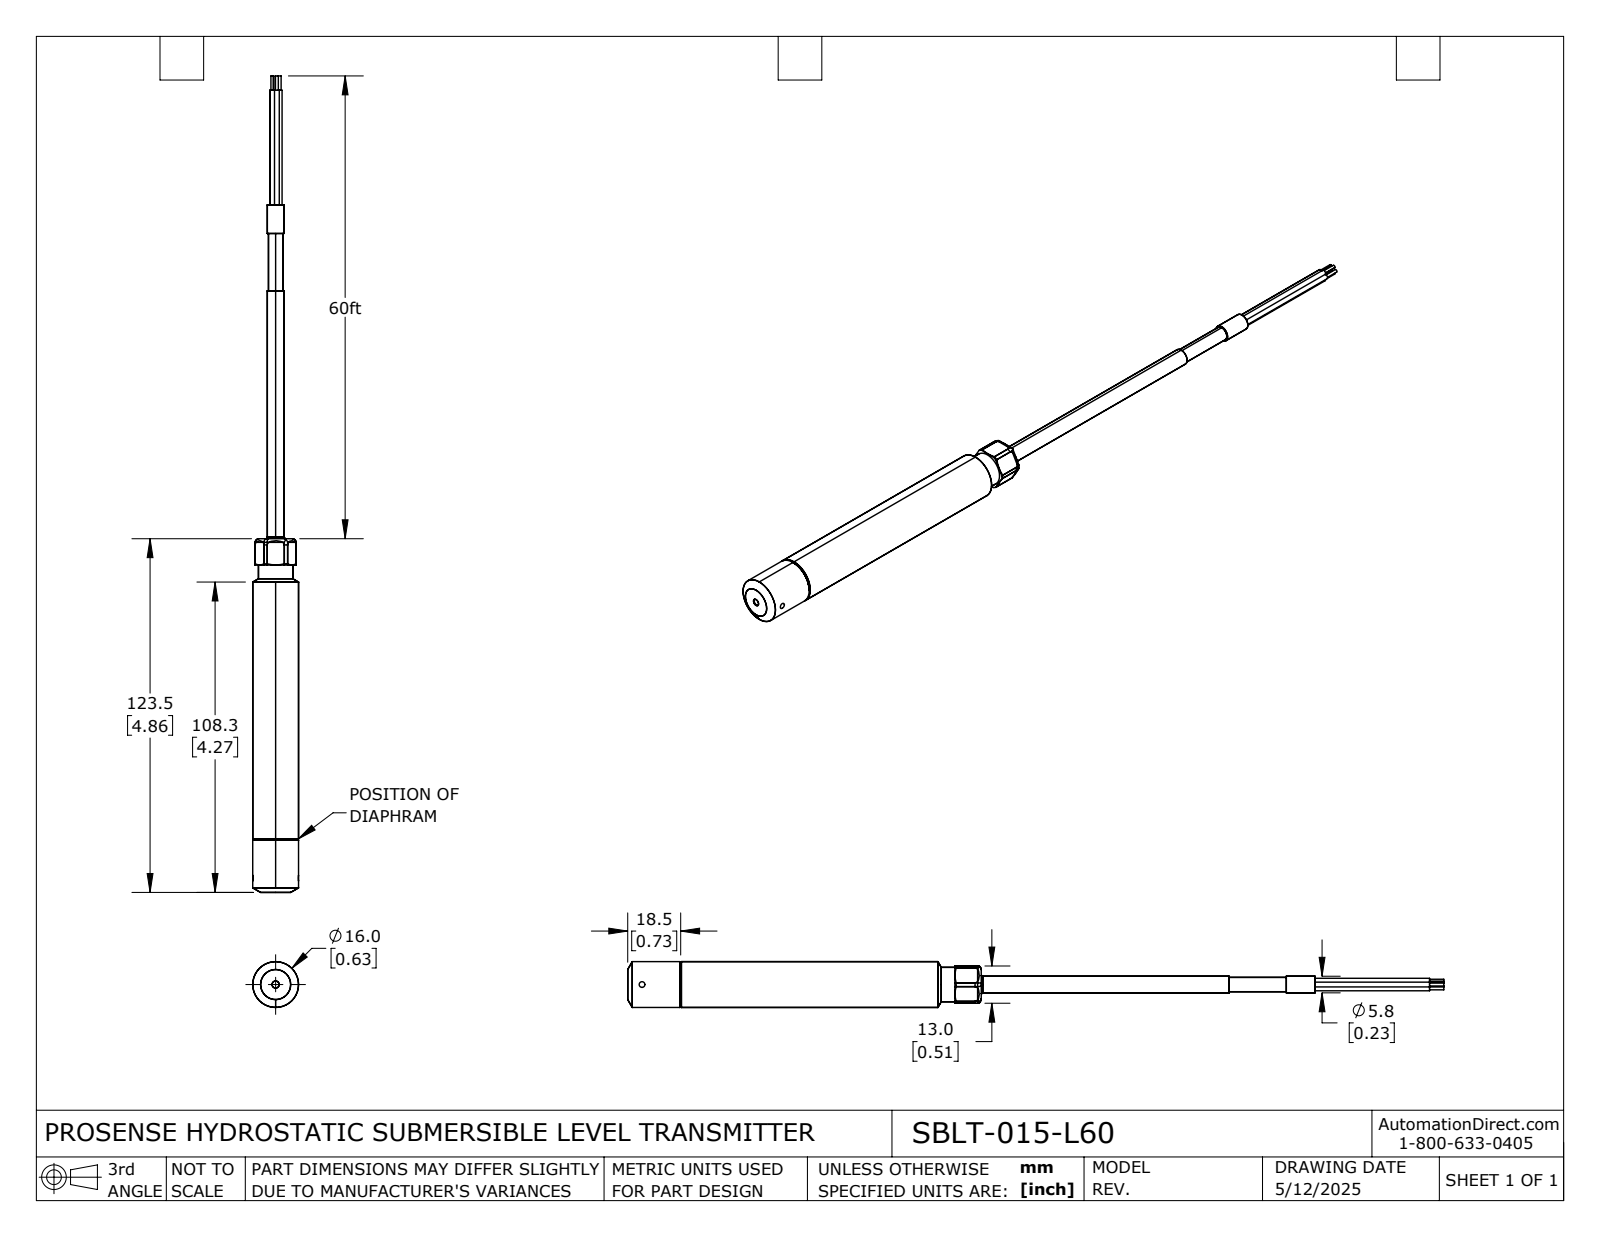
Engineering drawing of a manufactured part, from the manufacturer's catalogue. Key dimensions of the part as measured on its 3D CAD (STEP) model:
Part name (STEP PRODUCT): SBLT-015-L60
STEP written by: SolidWorks 2024 (AUTOMOTIVE_DESIGN)
Units: inches
Bodies: 11 solids, 201 faces (52 planar, 88 cylindrical, 61 other)
Overall size (bounding box): 11.221 × 0.63 × 0.63
Volume: 3.198 in³ · Surface area: 29.94 in²
Round holes (diameter × count): ⌀0.079 ×1, ⌀0.098 ×1, ⌀0.374 ×1, ⌀0.516 ×1, ⌀0.551 ×1
Round bosses / shafts (diameter × count): ⌀0.066 ×5, ⌀0.039 ×5, ⌀0.63 ×1, ⌀0.629 ×1, ⌀0.472 ×1, ⌀0.472 ×1, ⌀0.244 ×1, ⌀0.228 ×1
Partial cylindrical surfaces — rounded edges, fillets, slot ends (radius × count): R0.05 ×6, R0.281 ×1
Main face-to-face distances: 0.512, 4.861, 4.33, 0.531, 4.589, 8.918, 9.45, 3.77, 0.197, 8.721
